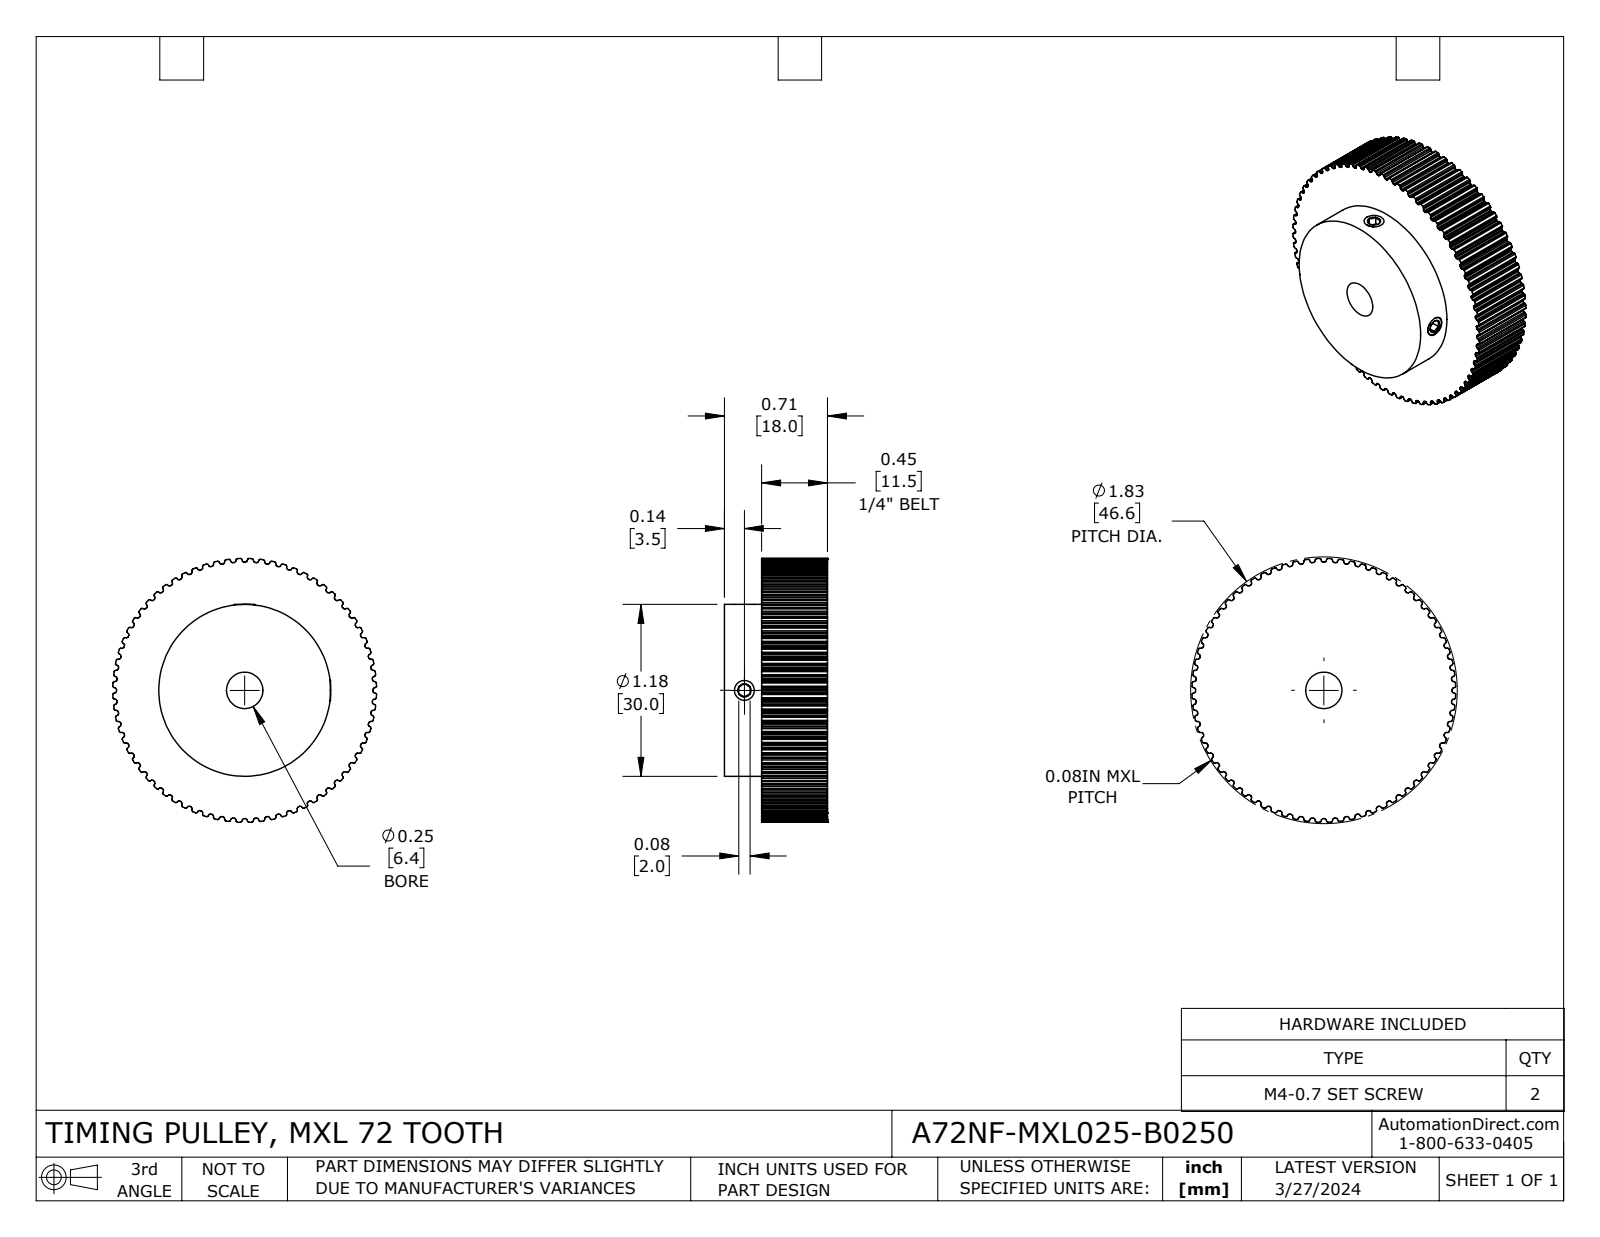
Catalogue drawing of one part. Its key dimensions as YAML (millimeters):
part_name: "A72NF-MXL025-B0250"
step_written_by: "SolidWorks 2021 (CONFIG_CONTROL_DESIGN)"
units: millimeters
bodies: {solids: 3, faces: 690, planar: 163, cylindrical: 501, other: 26}
overall_size: [46.04, 46.04, 18]
volume: 22567
surface_area: 6739
round_holes:
  - {diameter: 3.3, count: 2}
  - {diameter: 6.35, count: 1}
round_bosses_or_shafts:
  - {diameter: 4, count: 2}
  - {diameter: 30, count: 1}
partial_cylinders:
  - {radius: 0.23, count: 144}
  - {radius: 0.3, count: 144}
  - {radius: 22.39, count: 1}
  - {radius: 23.03, count: 1}
face_to_face_distances: [11.5, 18, 6.5, 14.68, 14.69, 14.7, 14.66, 2, 22.34, 7.66]
